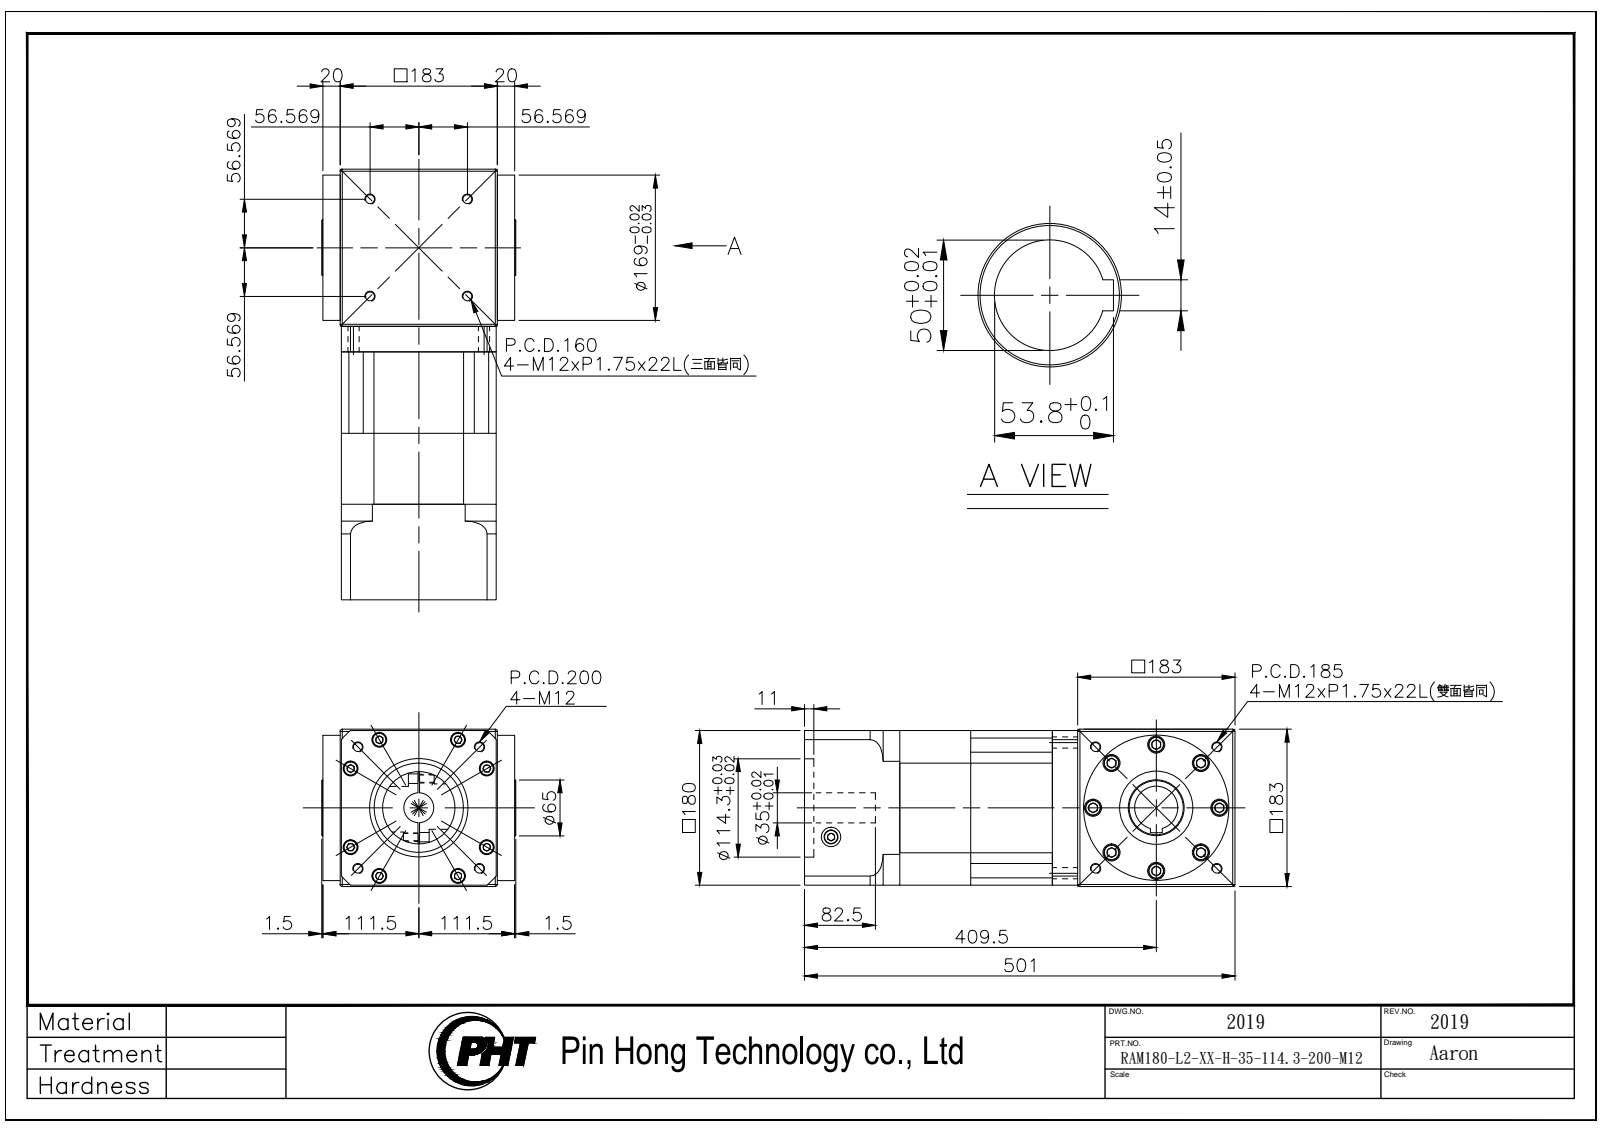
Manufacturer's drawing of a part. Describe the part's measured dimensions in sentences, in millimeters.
The part is named "RAM180-L2-XX-H-35-114.3-200-M12_2019". Its 3-D file was written by "SolidWorks 2016 (AUTOMOTIVE_DESIGN)". It is 5 solids with 798 faces: 354 planar, 280 cylindrical and 164 other. Overall it measures 501 by 226 by 183 millimeters. Its volume is 15 800 000 cubic millimeters and its surface area 909 960 square millimeters. Round holes: 20 of diameter 10.2, 8 of diameter 11, 8 of diameter 14, 8 of diameter 17, 8 of diameter 20, 4 of diameter 13, 2 of diameter 22.5, 1 of diameter 35, 1 of diameter 50, 1 of diameter 51, 1 of diameter 104, 1 of diameter 114.3. Round bosses or shafts: 8 of diameter 18.3, 8 of diameter 16, 4 of diameter 18, 1 of diameter 169, 1 of diameter 160, 1 of diameter 85, 1 of diameter 84, 1 of diameter 65. Partial cylindrical surfaces (rounded edges, fillets, slot ends): 4 of radius 12.5, 1 of radius 104, 1 of radius 105, 1 of radius 120. The main face-to-face distances are 181.5, 1.5, 180, 183, 82.5, 177.5, 95, 207, 124.5, 29.5. The hole center spacings are 91.5, 25.12, 26.38, 30.43, 56.25, 65.91, 73.5, 103.94.
